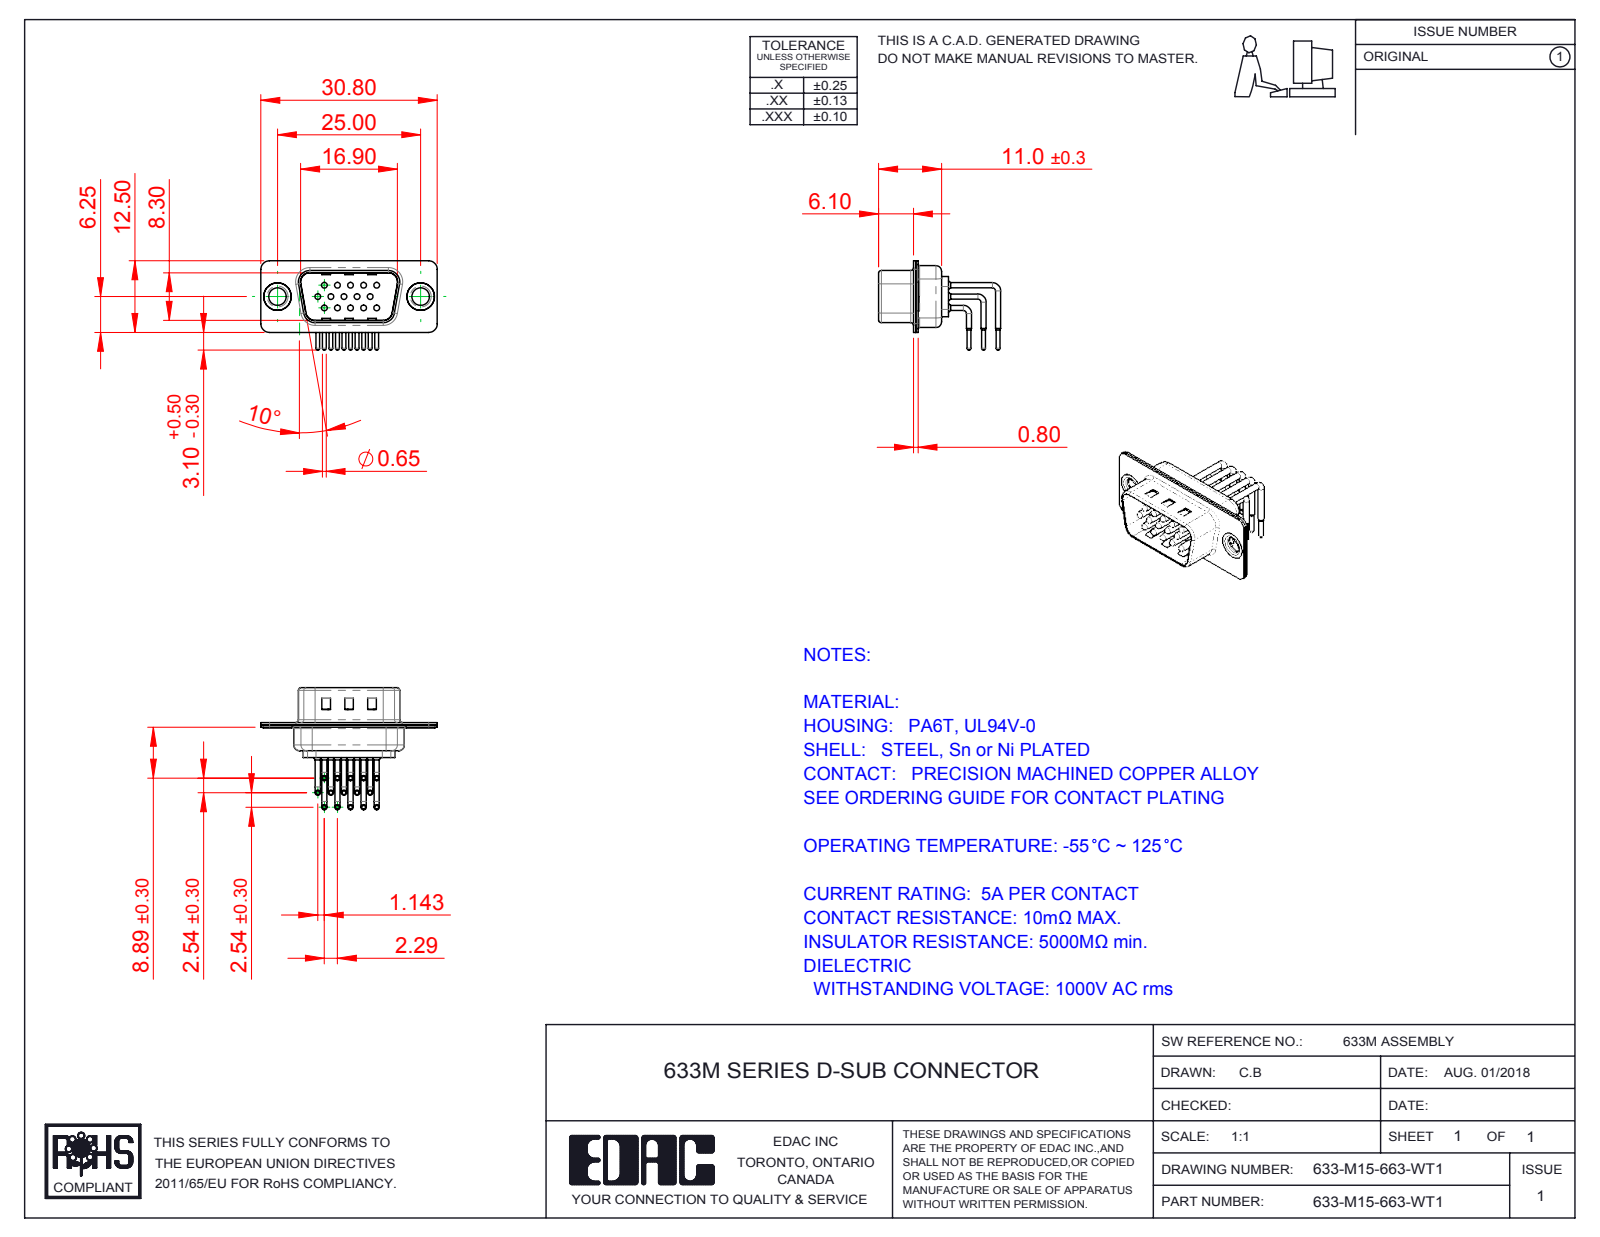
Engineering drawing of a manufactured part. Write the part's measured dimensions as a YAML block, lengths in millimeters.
part_name: "633M Contact Row 2; 633M Shell Rear_15 Contacts; 633M Thru Hole Rivet; 633M Shell Front_15 Contacts (+4 more)"
step_written_by: "SolidWorks 2016 (CONFIG_CONTROL_DESIGN)"
units: millimeters
bodies: {solids: 20, faces: 1928, planar: 1067, cylindrical: 653, other: 208}
overall_size: [30.8, 21.32, 15.6]
volume: 1371
surface_area: 4480
round_holes:
  - {diameter: 1, count: 15}
  - {diameter: 1.7, count: 15}
  - {diameter: 2, count: 15}
  - {diameter: 3.05, count: 2}
  - {diameter: 4, count: 2}
  - {diameter: 4.8, count: 2}
round_bosses_or_shafts:
  - {diameter: 0.9, count: 30}
  - {diameter: 1.5, count: 15}
  - {diameter: 0.65, count: 15}
  - {diameter: 5, count: 2}
  - {diameter: 4.9, count: 2}
  - {diameter: 3.55, count: 2}
partial_cylinders:
  - {radius: 1.5, count: 16}
  - {radius: 1.01, count: 15}
  - {radius: 2, count: 12}
  - {radius: 0.5, count: 8}
  - {radius: 1.6, count: 8}
  - {radius: 0.25, count: 4}
  - {radius: 0.6, count: 4}
  - {radius: 0.65, count: 4}
face_to_face_distances: [0.4, 0.85, 0.8, 9.55, 1.25, 10.4, 1.5, 8.7, 1.9, 0.35]
hole_center_spacings: [3.96, 2.28, 2.29, 4.57, 6.05, 6.86, 7.92, 6.04]
